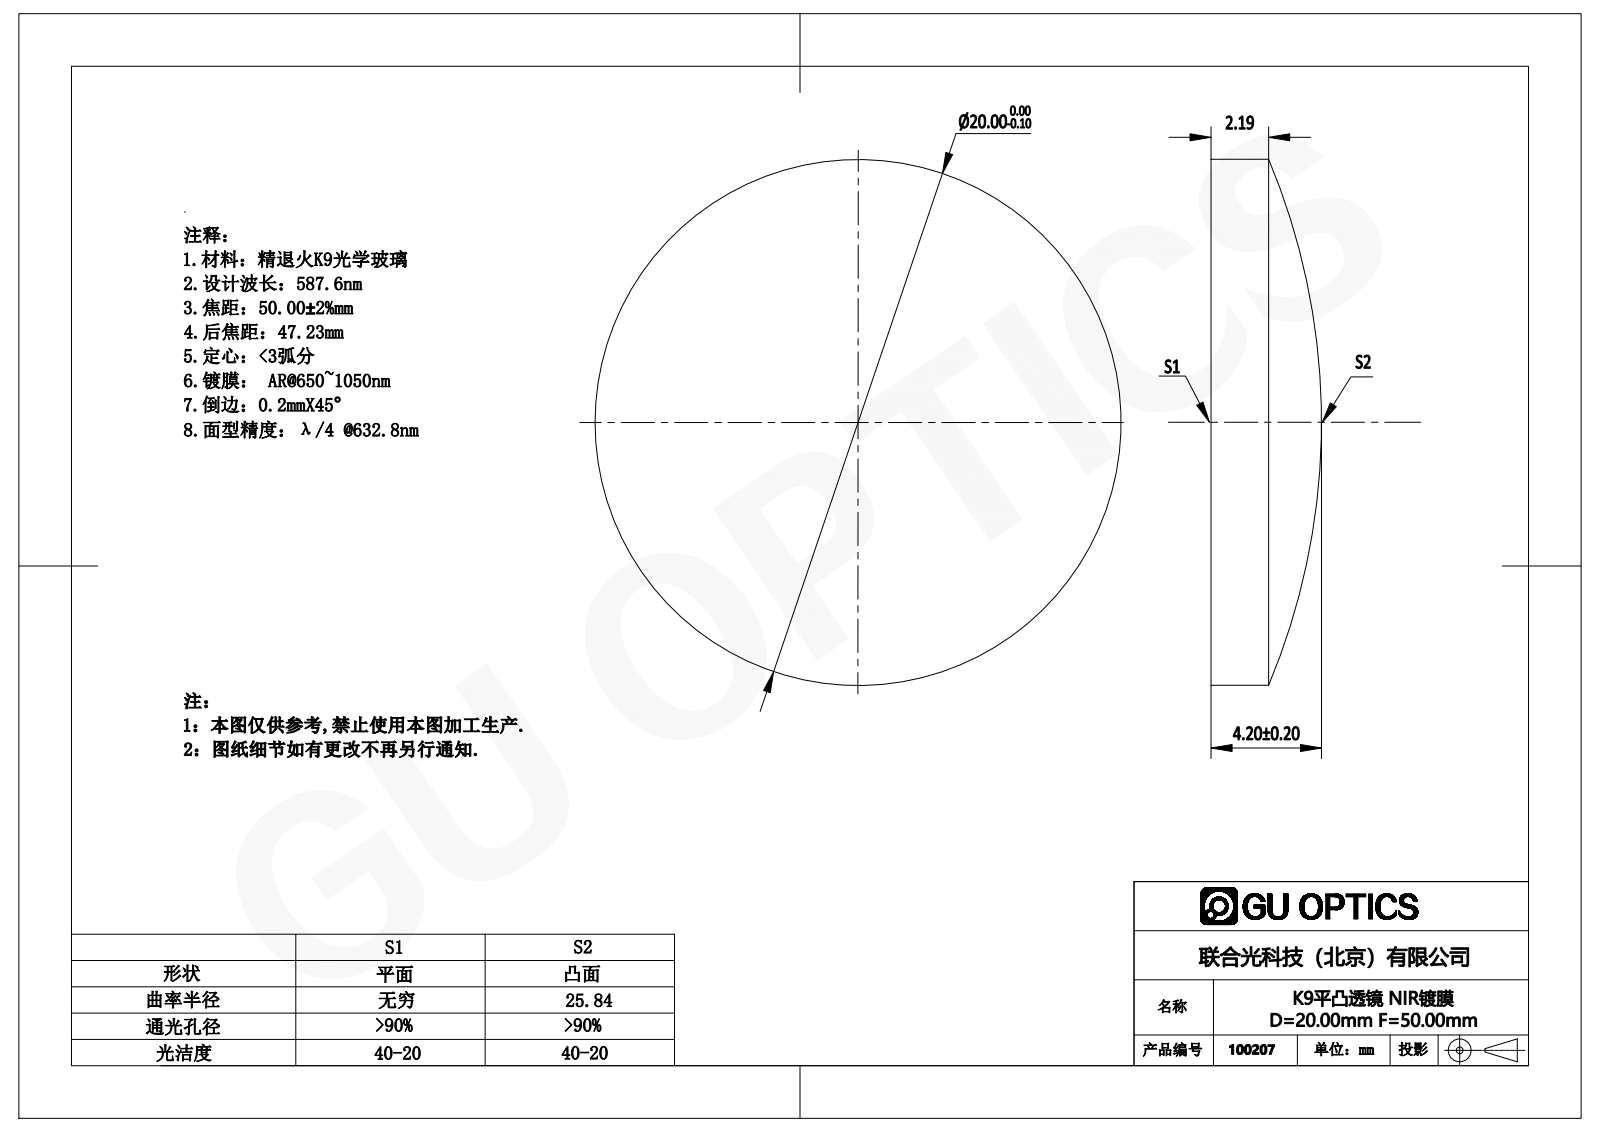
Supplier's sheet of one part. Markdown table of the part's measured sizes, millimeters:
| quantity | value |
| --- | --- |
| part name | 100207 |
| STEP written by | SolidWorks 2016 (AUTOMOTIVE_DESIGN) |
| units | millimeters |
| bodies | 1 solid, 5 faces (1 planar, 2 cylindrical, 2 other) |
| overall size | 20 × 20 × 4.2 |
| volume | 1 008 mm³ |
| surface area | 779 mm² |
| round bosses / shafts (diameter × count) | 20 × 1 |
